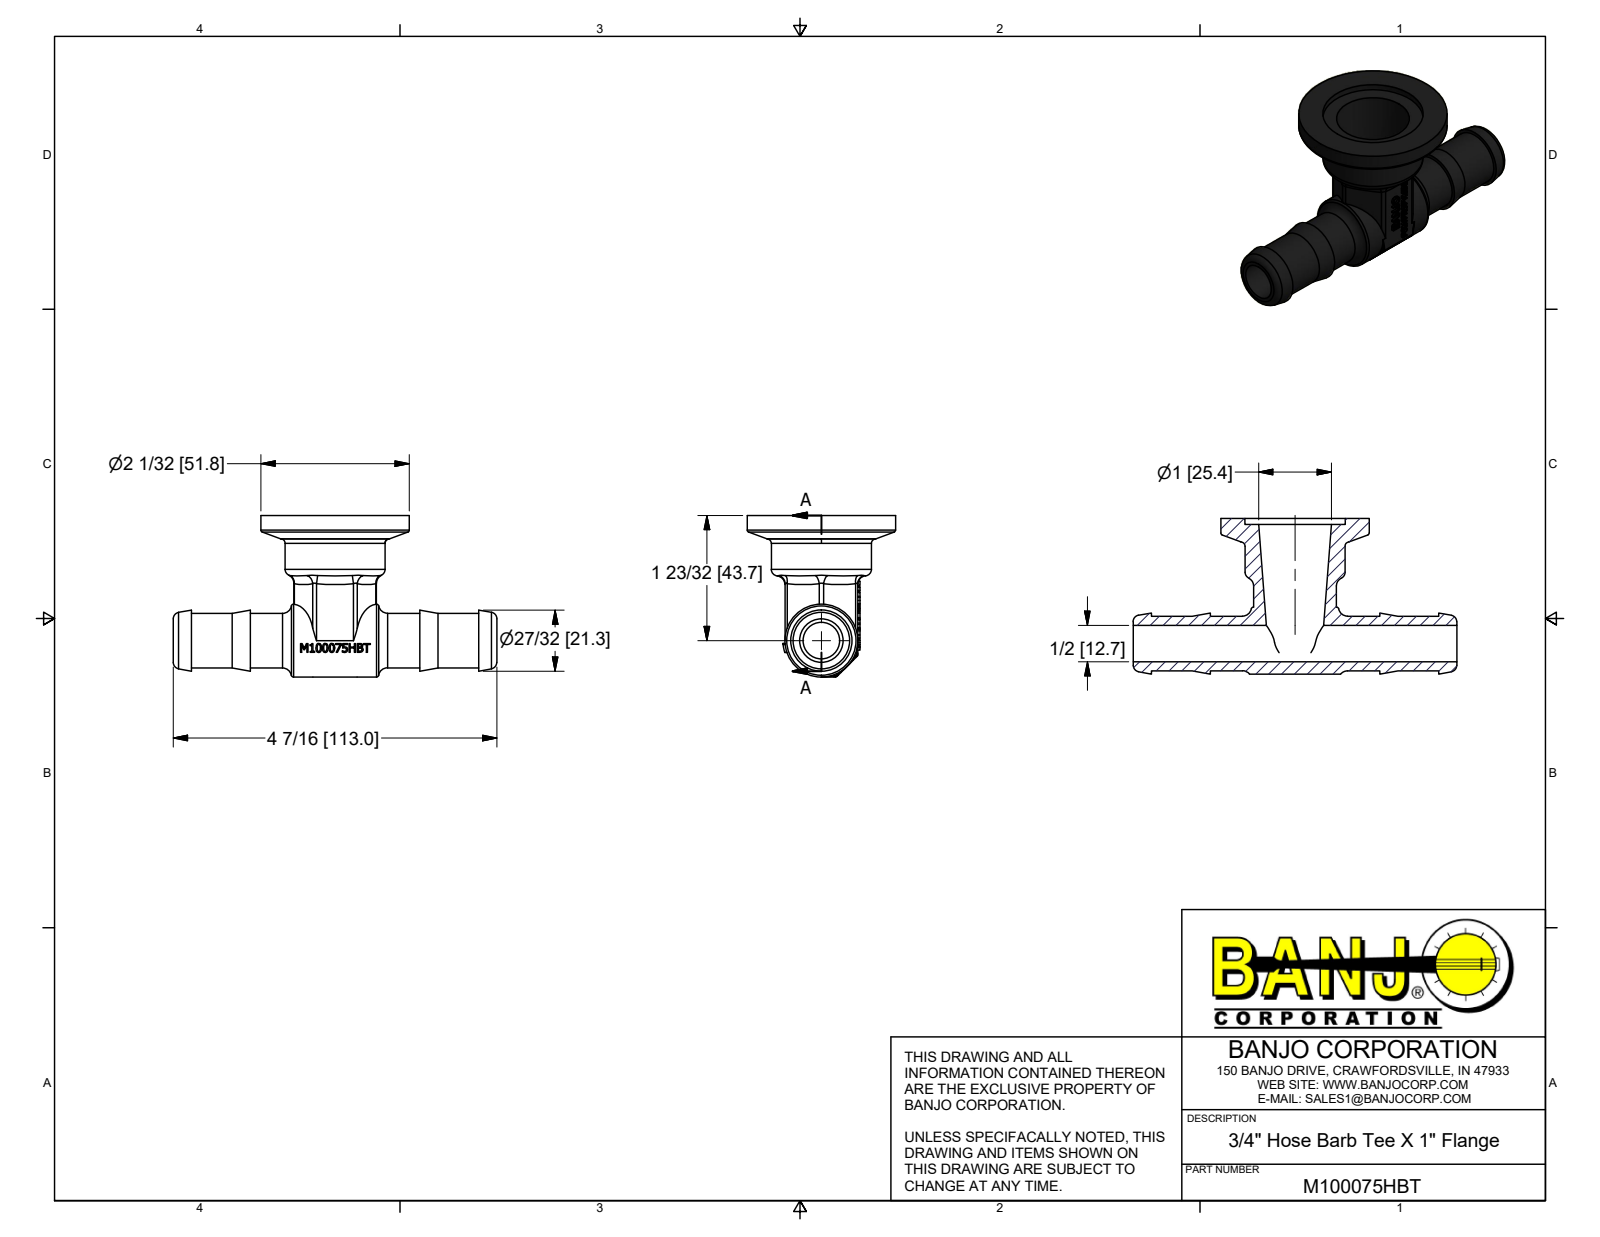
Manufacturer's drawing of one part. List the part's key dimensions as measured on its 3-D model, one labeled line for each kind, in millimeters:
Part name (STEP PRODUCT): M100075HBTU
STEP written by: Autodesk Inventor 2017 (AUTOMOTIVE_DESIGN)
Units: millimetres
Bodies: 1 solid, 507 faces (251 planar, 41 cylindrical, 215 other)
Overall size (bounding box): 113.03 × 56.39 × 51.82
Volume: 43 680 mm³ · Surface area: 21 606 mm²
Round holes (diameter × count): ⌀12.7 ×1, ⌀35.05 ×1
Round bosses / shafts (diameter × count): ⌀51.82 ×1, ⌀34.92 ×1, ⌀25.4 ×1, ⌀19.05 ×1
Partial cylindrical surfaces — rounded edges, fillets, slot ends (radius × count): R0.38 ×6, R1.52 ×6, R0.76 ×2, R13.46 ×1
Main face-to-face distances: 25.4, 2.14, 20.57, 79.75, 6.36, 26.93, 86.11, 106.68, 100.32, 59.18
